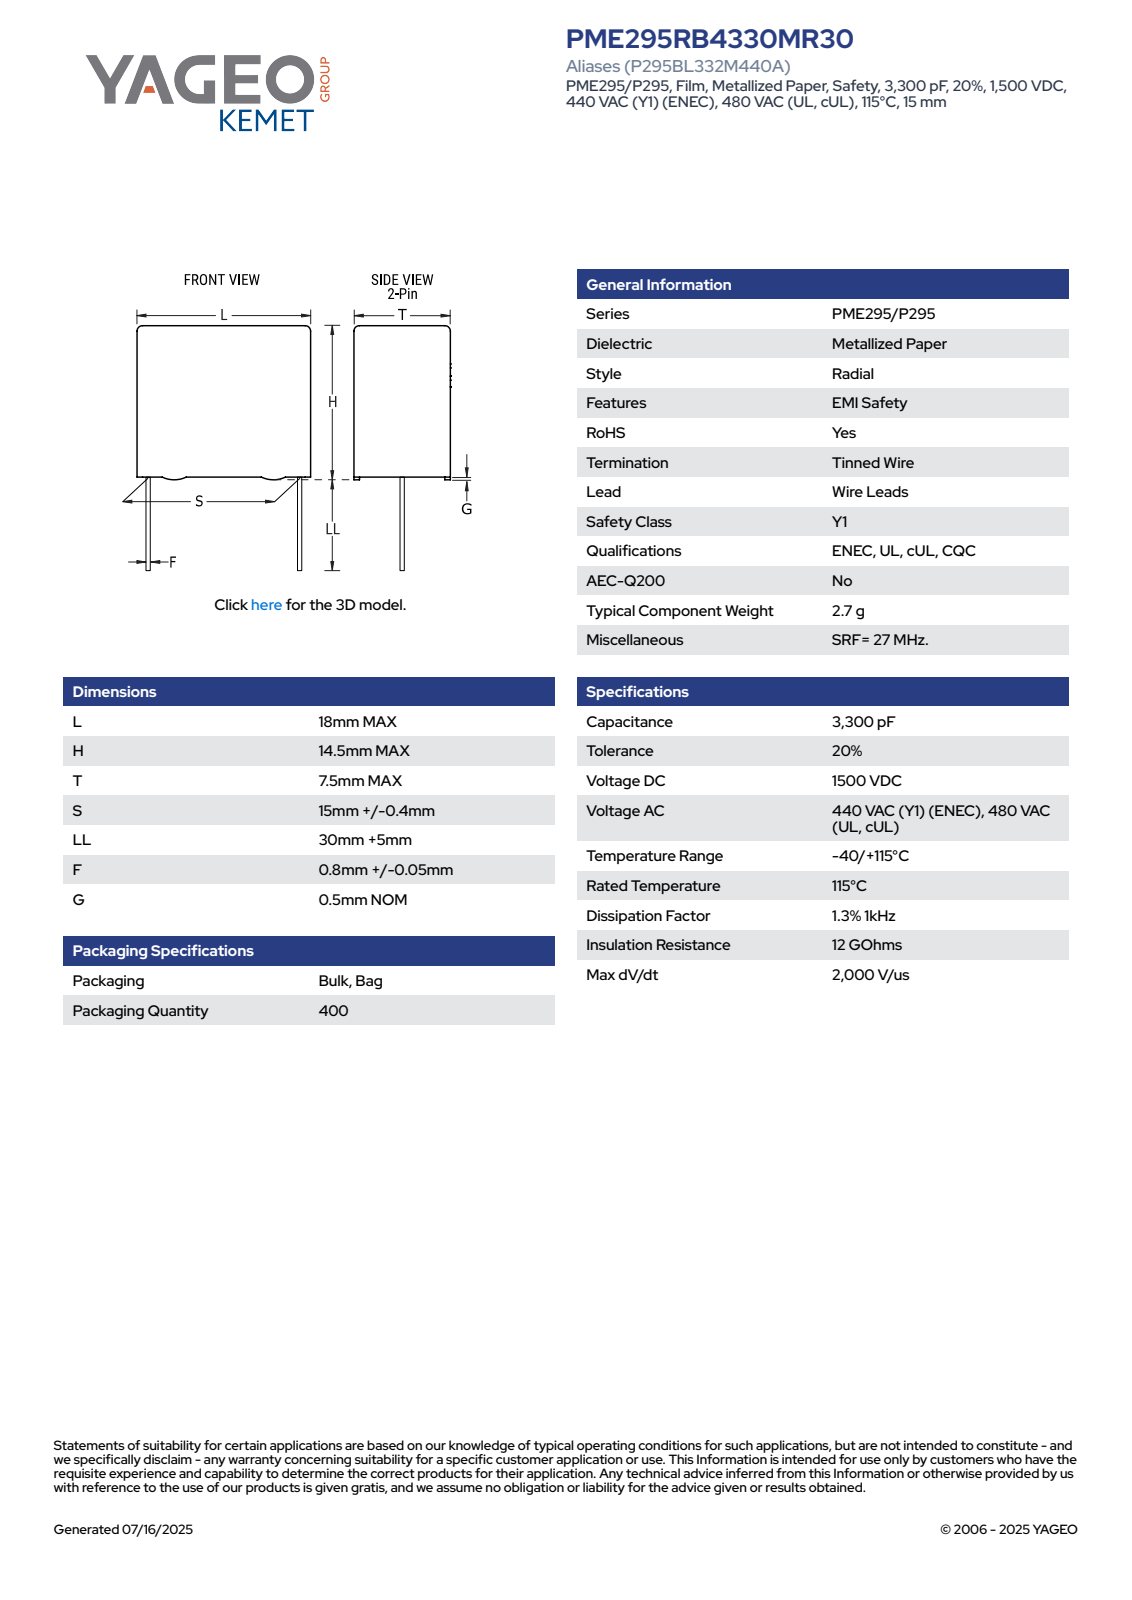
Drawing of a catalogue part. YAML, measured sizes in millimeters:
part_name: "CFR_RBG_18X14.5X7.5_L18H14.5T7.5S15LL35F0.85G0.5"
step_written_by: "SolidWorks 2014 (AUTOMOTIVE_DESIGN)"
units: millimeters
bodies: {solids: 4, faces: 89, planar: 81, cylindrical: 8, other: 0}
overall_size: [49.5, 18, 7.5]
volume: 1930
surface_area: 1210
round_bosses_or_shafts:
  - {diameter: 0.85, count: 2}
partial_cylinders:
  - {radius: 0.5, count: 4}
face_to_face_distances: [7.5, 14, 18, 0.43, 7.07, 0.5, 14.5, 6.64, 35, 35.5]
